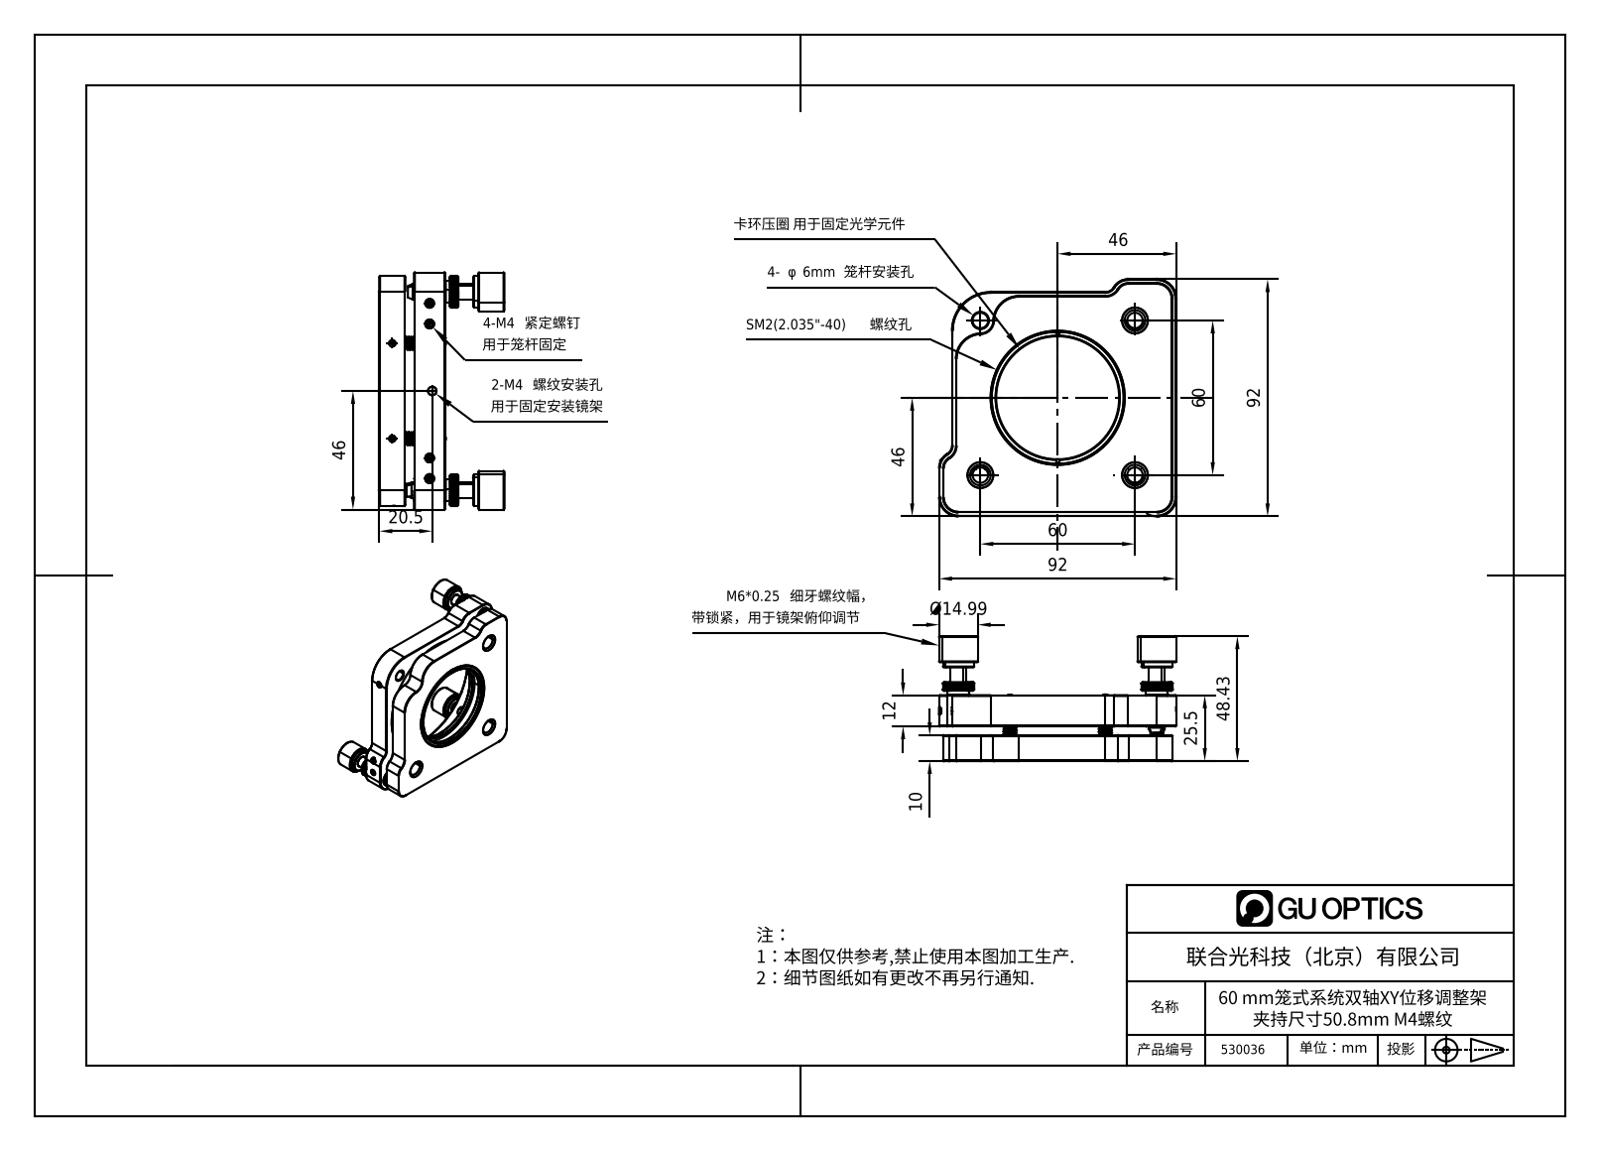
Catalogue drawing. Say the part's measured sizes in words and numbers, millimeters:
The part is named "2.3.3_igs". Its 3-D file was written by "SolidWorks 2020 (CONFIG_CONTROL_DESIGN)". It is 0 solids with 1217 faces: 460 planar, 298 cylindrical and 459 other. Overall it measures 92 by 92 by 48.43 millimeters. Round holes: 8 of diameter 6, 4 of diameter 3.3, 3 of diameter 4, 3 of diameter 8, 3 of diameter 10, 1 of diameter 5.5, 1 of diameter 47.69, 1 of diameter 47.69, 1 of diameter 51.05, 1 of diameter 73.5. Round bosses or shafts: 4 of diameter 2, 3 of diameter 15, 3 of diameter 12, 3 of diameter 8.6, 3 of diameter 6, 2 of diameter 9.5, 1 of diameter 4, 1 of diameter 1.5. Partial cylindrical surfaces (rounded edges, fillets, slot ends): 8 of radius 1.02, 3 of radius 5, 2 of radius 4, 2 of radius 5.5, 2 of radius 6.5, 2 of radius 10, 1 of radius 15. The main face-to-face distances are 10, 3.5, 12, 13.5, 15.5, 25.5, 1.5, 85.5, 87, 5. The hole center spacings are 69.03, 14.3, 20, 42.43, 42.71, 49.24, 57, 60.
